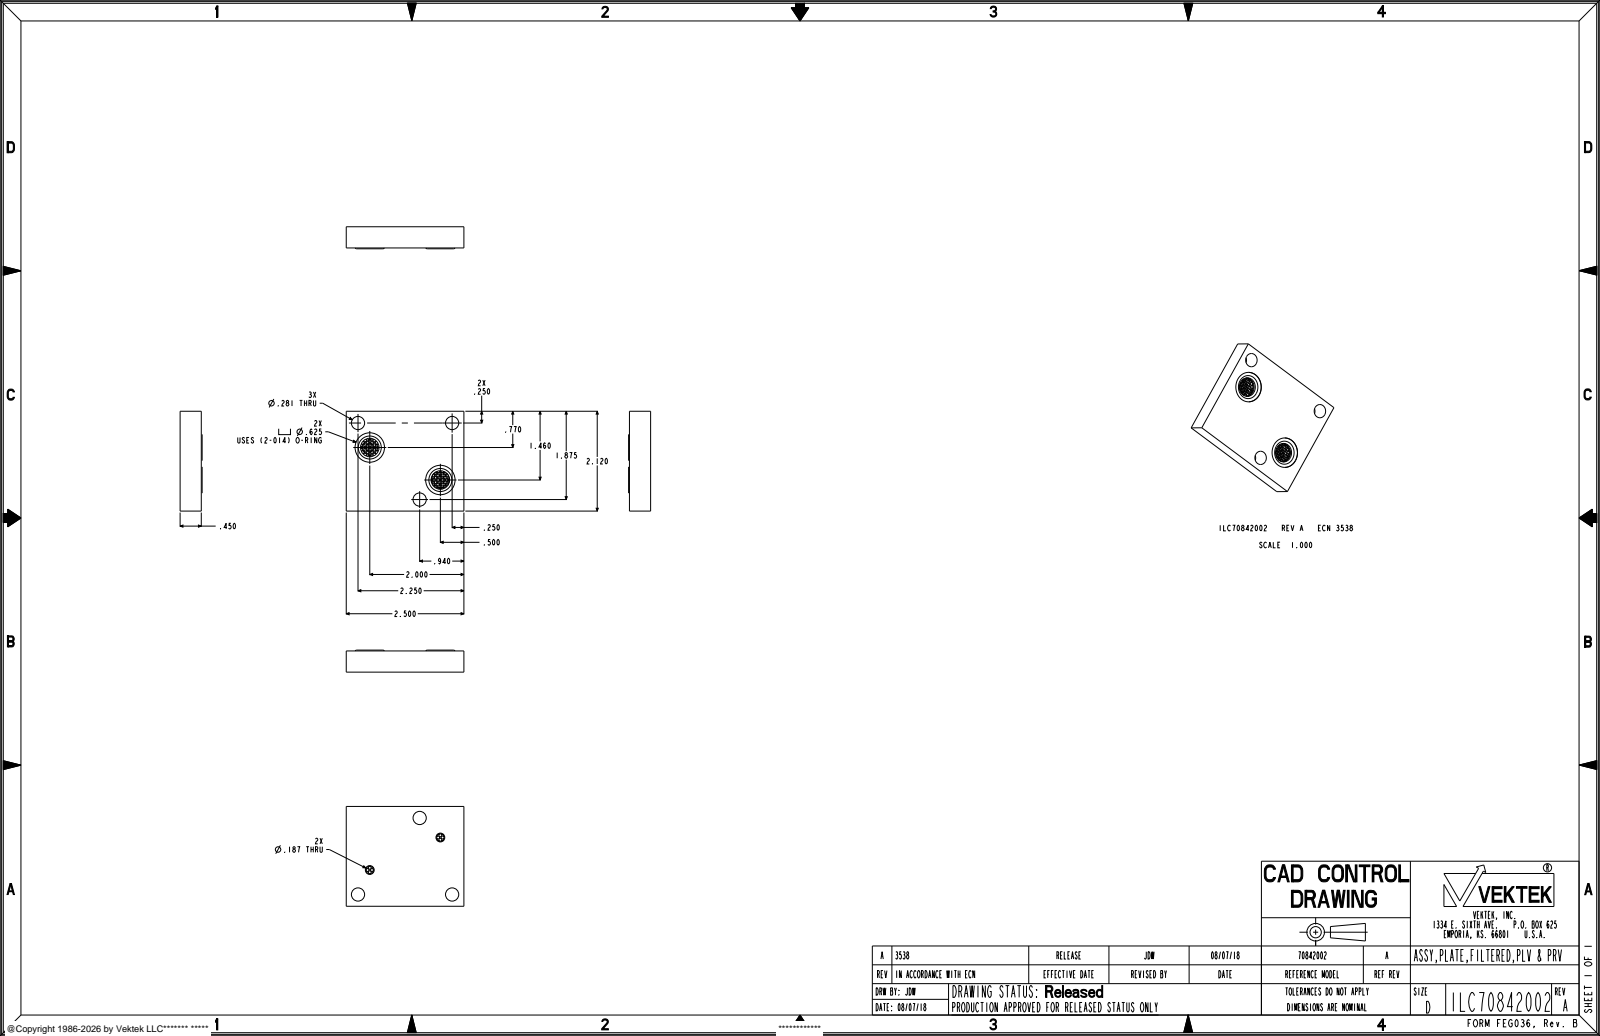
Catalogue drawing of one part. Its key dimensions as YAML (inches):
part_name: "ILC70842002"
step_written_by: "PRO/ENGINEER BY PARAMETRIC TECHNOLOGY CORPORATION, 2013320 (AUTOMOTIVE_DESIGN)"
units: inches
bodies: {solids: 2, faces: 341, planar: 40, cylindrical: 293, other: 8}
overall_size: [2.5, 2.12, 0.468]
volume: 2.204
surface_area: 18.05
round_holes:
  - {diameter: 0.062, count: 32}
  - {diameter: 0.281, count: 3}
  - {diameter: 0.187, count: 2}
  - {diameter: 0.393, count: 2}
  - {diameter: 0.411, count: 2}
  - {diameter: 0.625, count: 2}
partial_cylinders:
  - {radius: 0.031, count: 32}
  - {radius: 0.01, count: 2}
  - {radius: 0.015, count: 2}
  - {radius: 0.023, count: 2}
  - {radius: 0.187, count: 2}
  - {radius: 0.19, count: 1}
face_to_face_distances: [0.45, 2.12, 2.5, 0.398, 0.052, 0.196, 0.031, 0.082, 0.316, 0.368]
hole_center_spacings: [0.094, 0.148, 0.067, 0.133, 0.21, 1.651, 0.066, 0.105]
